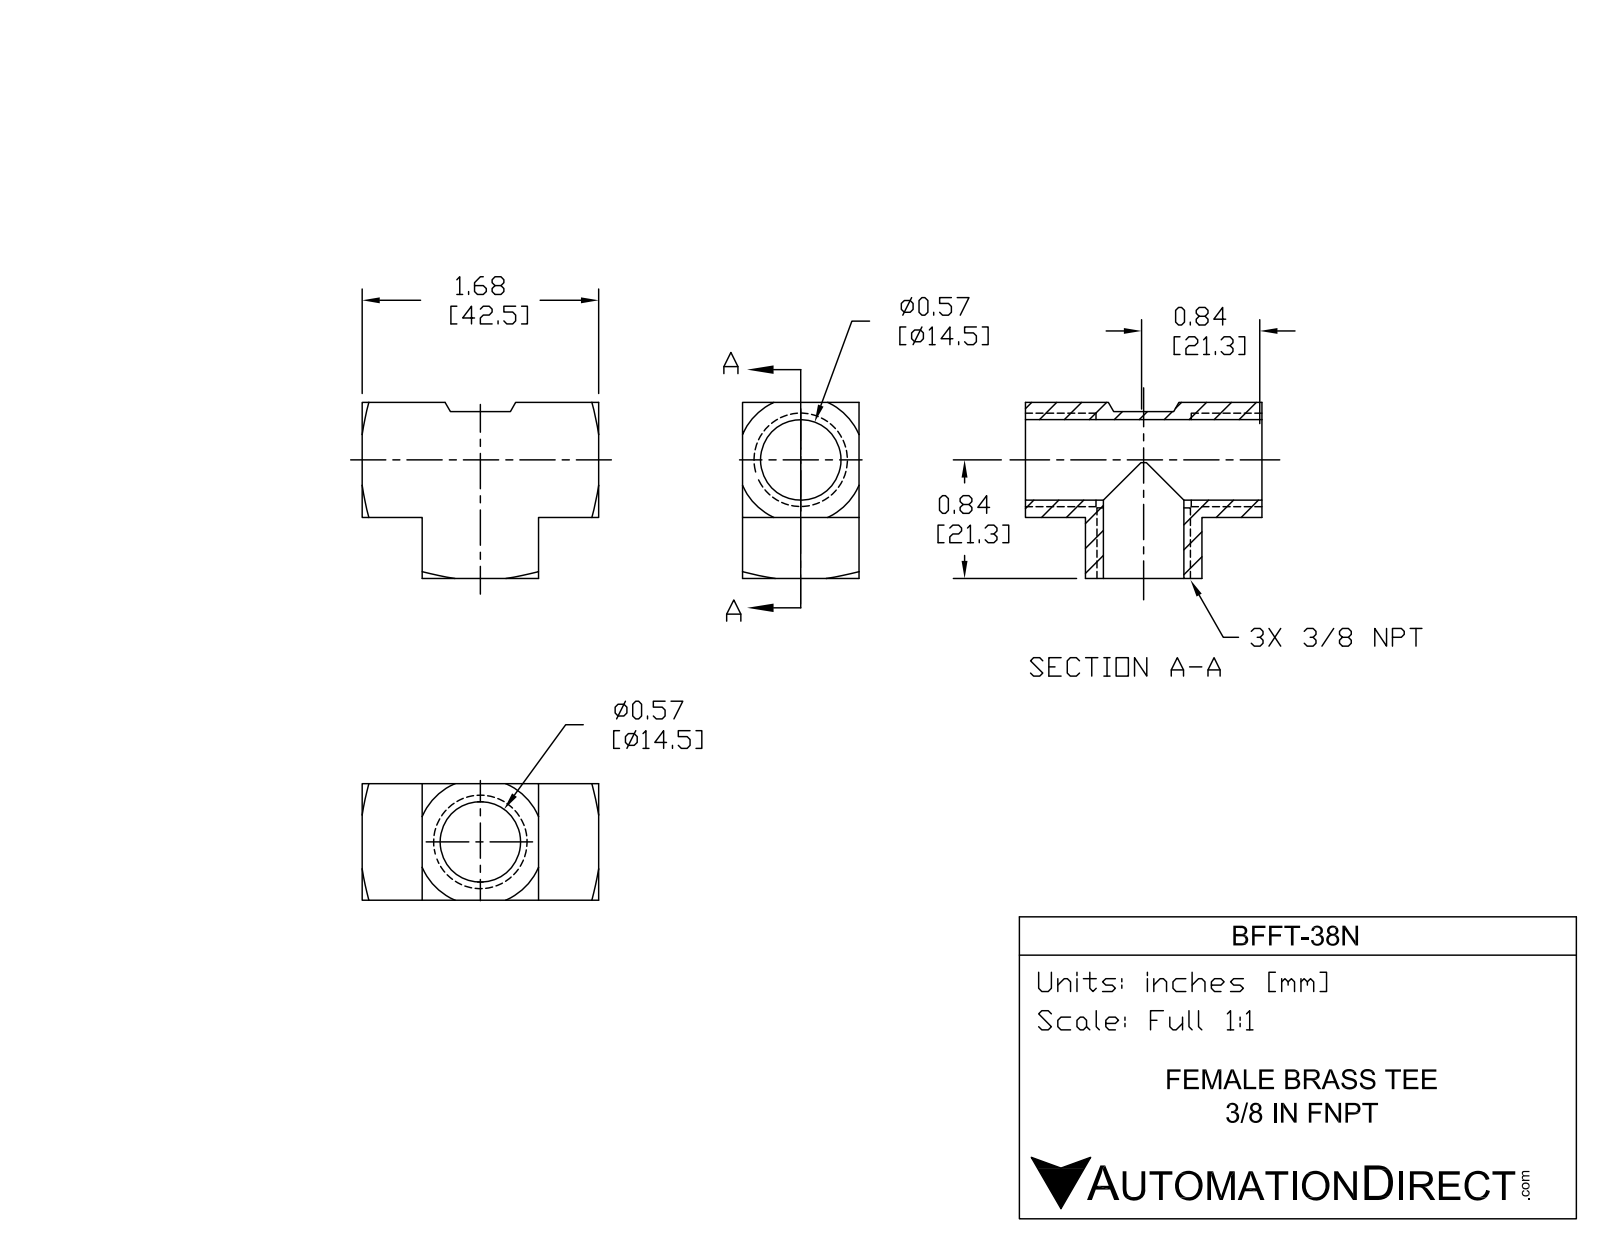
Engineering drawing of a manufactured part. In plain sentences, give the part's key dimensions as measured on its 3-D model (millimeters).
The part is named "BFFT-38N". Its 3-D file was written by "SolidWorks 2015 (CONFIG_CONTROL_DESIGN)". It is 1 solid with 32 faces: 16 planar, 4 cylindrical and 12 other. Overall it measures 42.5 by 31.7 by 21 millimeters. Its volume is 13 300 cubic millimeters and its surface area 7 258 square millimeters. Round holes: 2 of diameter 14.5. The main face-to-face distances are 21, 20.7, 10.8, 31.8, 1.7, 19.1, 21, 31.7, 30, 11.
